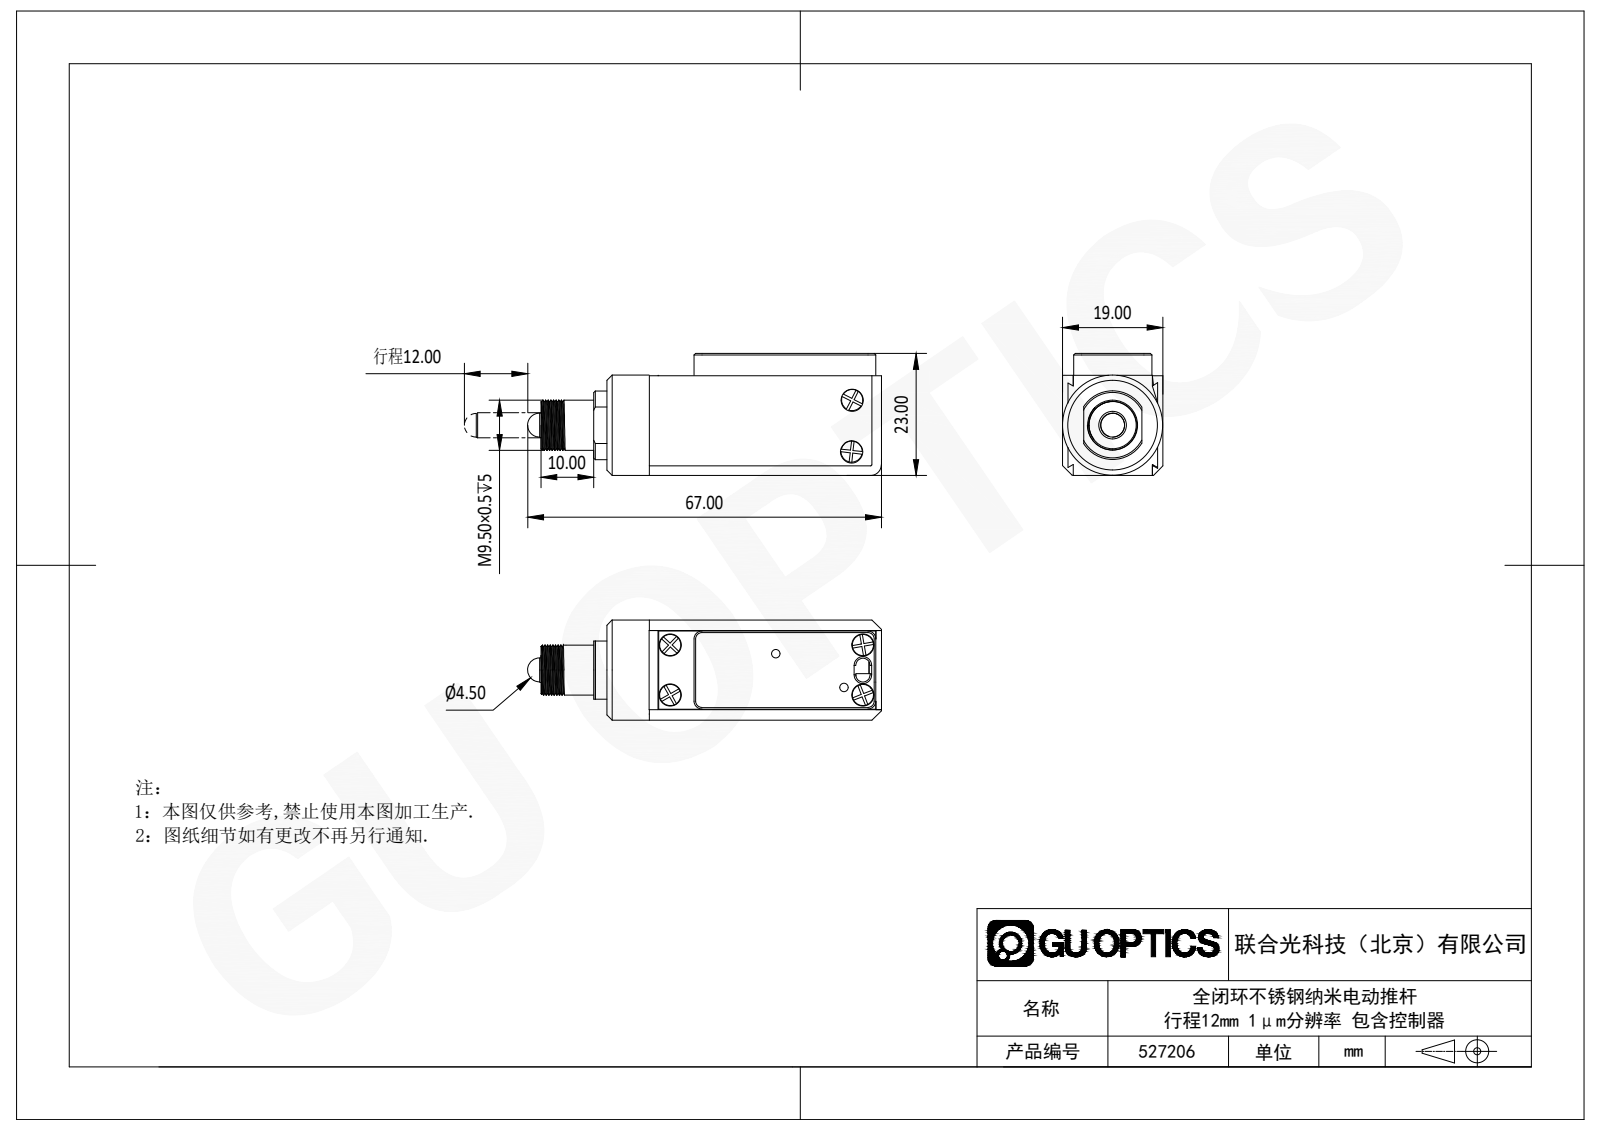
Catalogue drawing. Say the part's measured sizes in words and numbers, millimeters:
The part is named "527206". Its 3-D file was written by "SolidWorks 2020 (CONFIG_CONTROL_DESIGN)". It is 0 solids with 301 faces: 197 planar, 79 cylindrical and 25 other. Overall it measures 67 by 23.1 by 19 millimeters. Round holes: 4 of diameter 4.2, 3 of diameter 4, 1 of diameter 9.5, 1 of diameter 19. Round bosses or shafts: 4 of diameter 4.2, 3 of diameter 4, 2 of diameter 1.6, 1 of diameter 5.2, 1 of diameter 2.5. Partial cylindrical surfaces (rounded edges, fillets, slot ends): 8 of radius 1.5, 2 of radius 1.35, 2 of radius 2, 2 of radius 2.1, 1 of radius 6.5. The main face-to-face distances are 17, 1, 2, 19, 18, 16, 15, 1.1, 2.1, 16.9. The hole center spacings are 7.27, 27.91, 9.5, 22.
